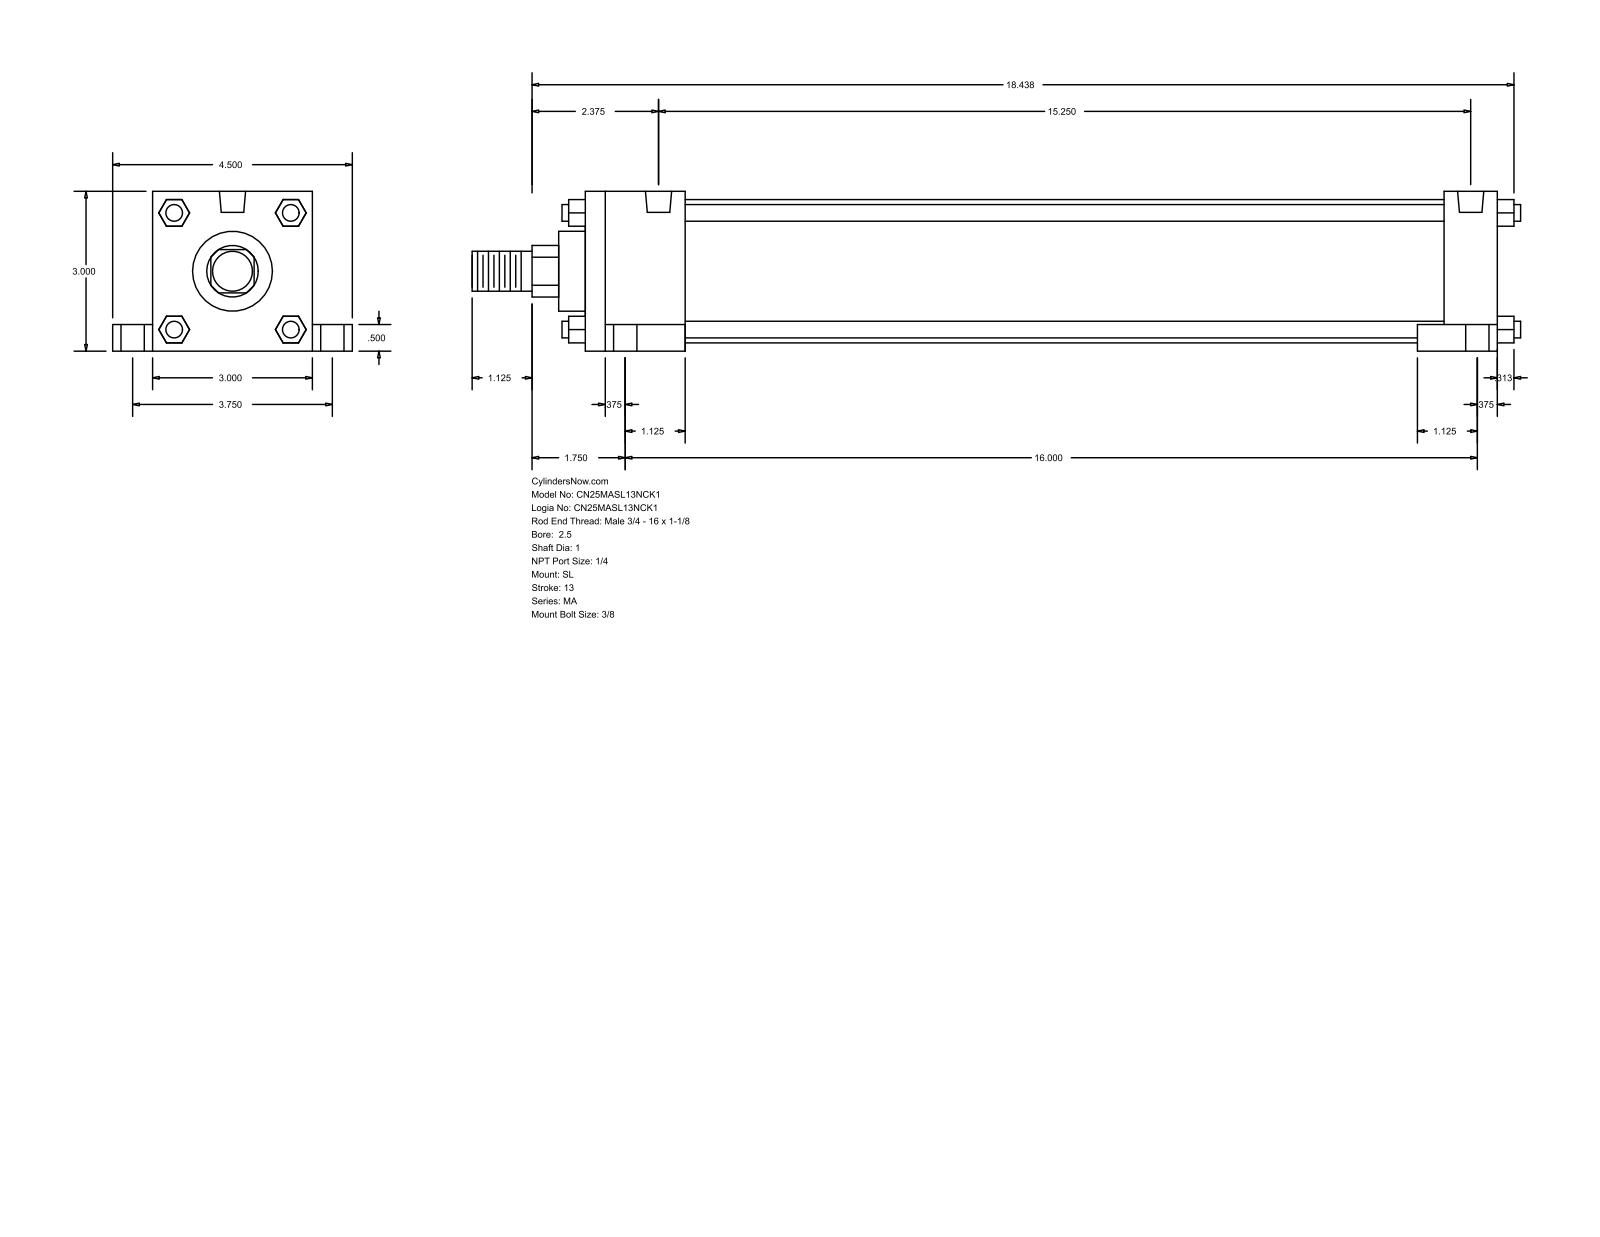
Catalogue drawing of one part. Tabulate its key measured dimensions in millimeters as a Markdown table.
| quantity | value |
| --- | --- |
| part name | MA_SL__0250_1 |
| STEP written by | GSSL Pune (CONFIG_CONTROL_DESIGN) |
| units | millimeters |
| bodies | 0 solids, 148 faces (112 planar, 36 cylindrical, 0 other) |
| overall size | 500.06 × 114.3 × 76.2 |
| round holes (diameter × count) | 7.94 × 4, 11.11 × 4, 17.46 × 4, 12.49 × 2 |
| round bosses / shafts (diameter × count) | 7.94 × 4, 68.33 × 1, 38.1 × 1, 25.4 × 1, 19.05 × 1 |
| partial cylindrical surfaces (radius × count) | 12.29 × 1 |
| main face-to-face distances | 76.2, 434.98, 12.7, 361.95, 25.4, 47.63, 387.35, 409.58, 19.05, 95.25 |
| hole center spacings | 47.73, 50.2, 95.24, 387.35, 393.41, 406.03, 406.4, 417.41 |
